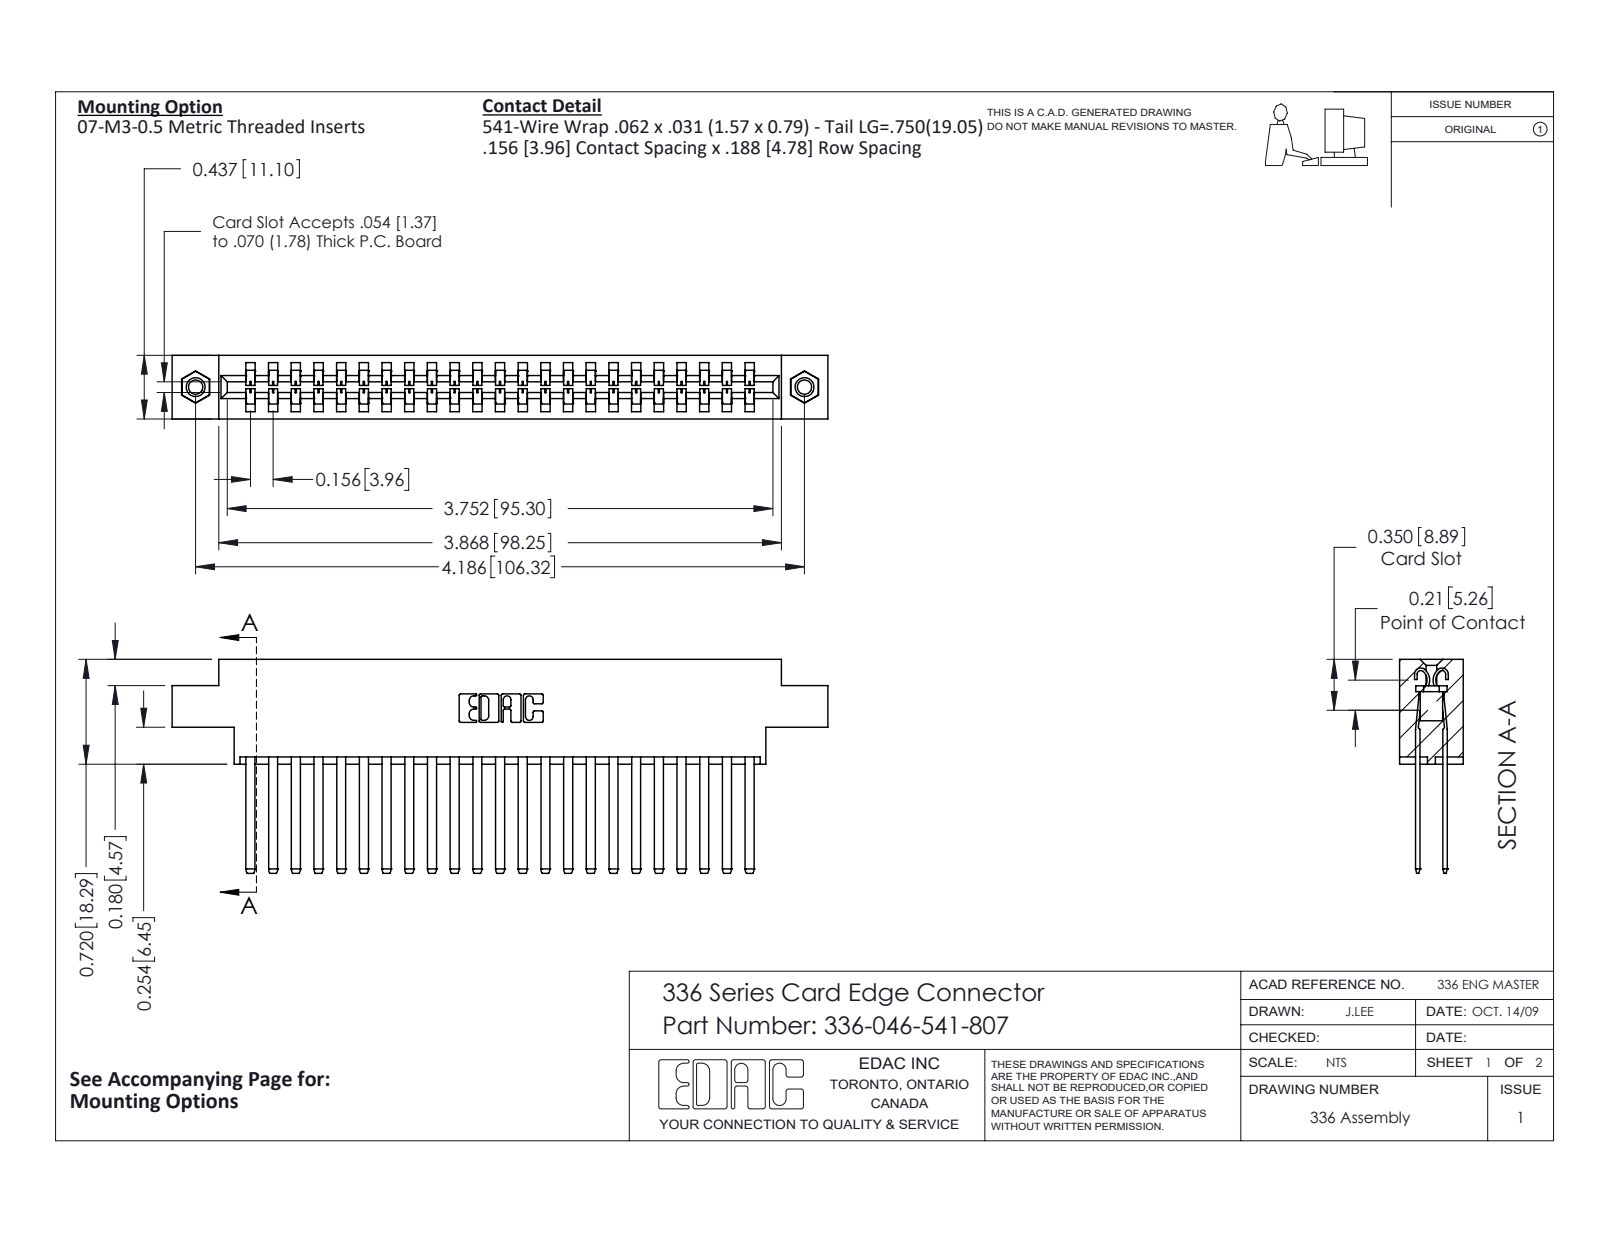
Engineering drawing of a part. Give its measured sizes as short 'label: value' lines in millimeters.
name: 336-290-001_336-290-541; 336-046-541-807; 345-250-001_345-250-005-103; 336 Part_Offset - .156 Dia - TI
written by: SolidWorks 2020 (CONFIG_CONTROL_DESIGN)
unit: mm
bodies: 49 solids, 2110 faces (1302 planar, 792 cylindrical, 16 other)
size: 114.5 × 37.3 × 11.1
volume: 17 060 mm³; area: 21 550 mm²
holes: 2× ⌀2.5, 2× ⌀3.2, 2× ⌀4
bosses: 2× ⌀3.9
rounds: 92× R0.1, 46× R1.4, 22× R0.3, 6× R0.2, 6× R0.8, 4× R0.6, 4× R1, 3× R0.7
face distances: 4.8, 8.3, 3.6, 7.5, 2.8, 0.8, 11.1, 0.8, 4, 4.6
hole spacings: 106.3
